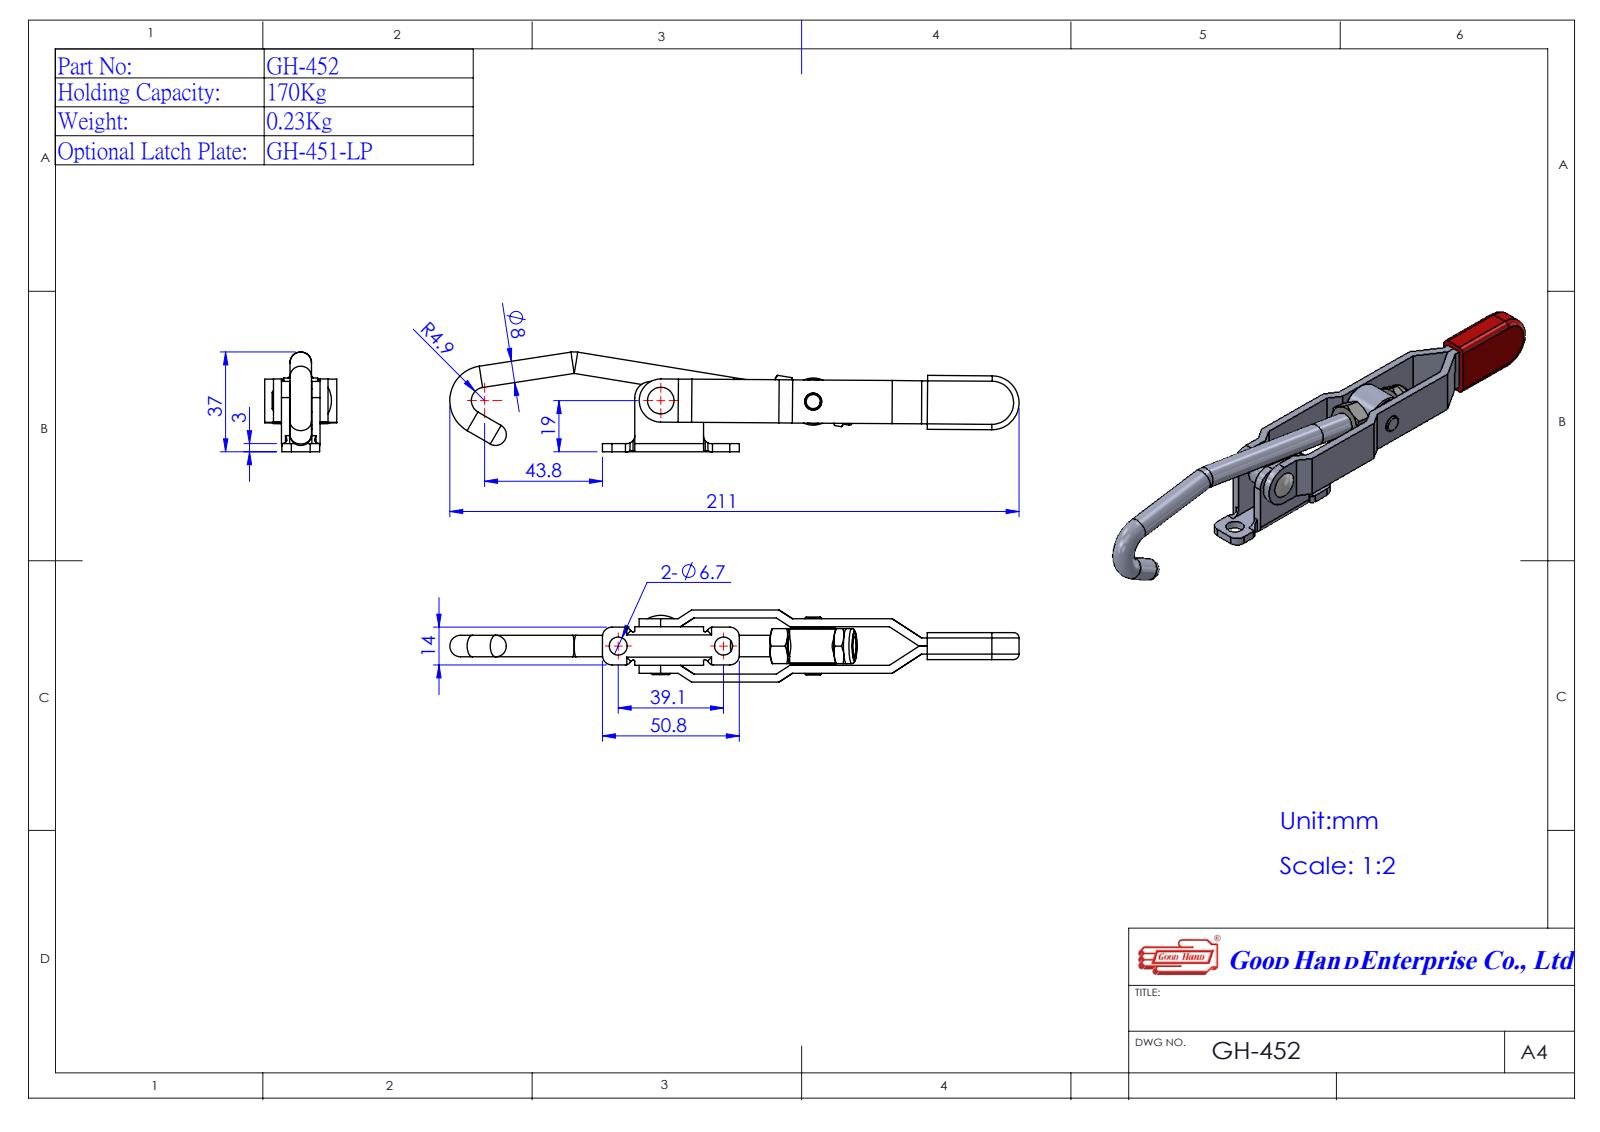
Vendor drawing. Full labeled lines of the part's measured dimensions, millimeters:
Part name (STEP PRODUCT): 445144-1^GH-452(簡化); Group2^GH-452(簡化); Group3^GH-452(簡化); GH-452(簡化) (+1 more)
STEP written by: SolidWorks 2016 (AUTOMOTIVE_DESIGN)
Units: millimetres
Bodies: 6 solids, 201 faces (81 planar, 74 cylindrical, 46 other)
Overall size (bounding box): 212.03 × 36.5 × 26.71
Volume: 35 083 mm³ · Surface area: 22 601 mm²
Round holes (diameter × count): ⌀8 ×3, ⌀6.7 ×2, ⌀6.8 ×2, ⌀5 ×1, ⌀6.2 ×1, ⌀9.43 ×1
Round bosses / shafts (diameter × count): ⌀8 ×3, ⌀17.5 ×1, ⌀13 ×1, ⌀9.5 ×1
Partial cylindrical surfaces — rounded edges, fillets, slot ends (radius × count): R2 ×5, R0.5 ×4, R3 ×4, R3.5 ×4, R2.08 ×2, R2.21 ×1, R2.5 ×1, R6 ×1
Main face-to-face distances: 2.96, 3.25, 20.51, 3, 17.26, 14.3, 5.11, 15.11, 2.15, 12.15
Hole centre spacings: 39.1, 56.6
